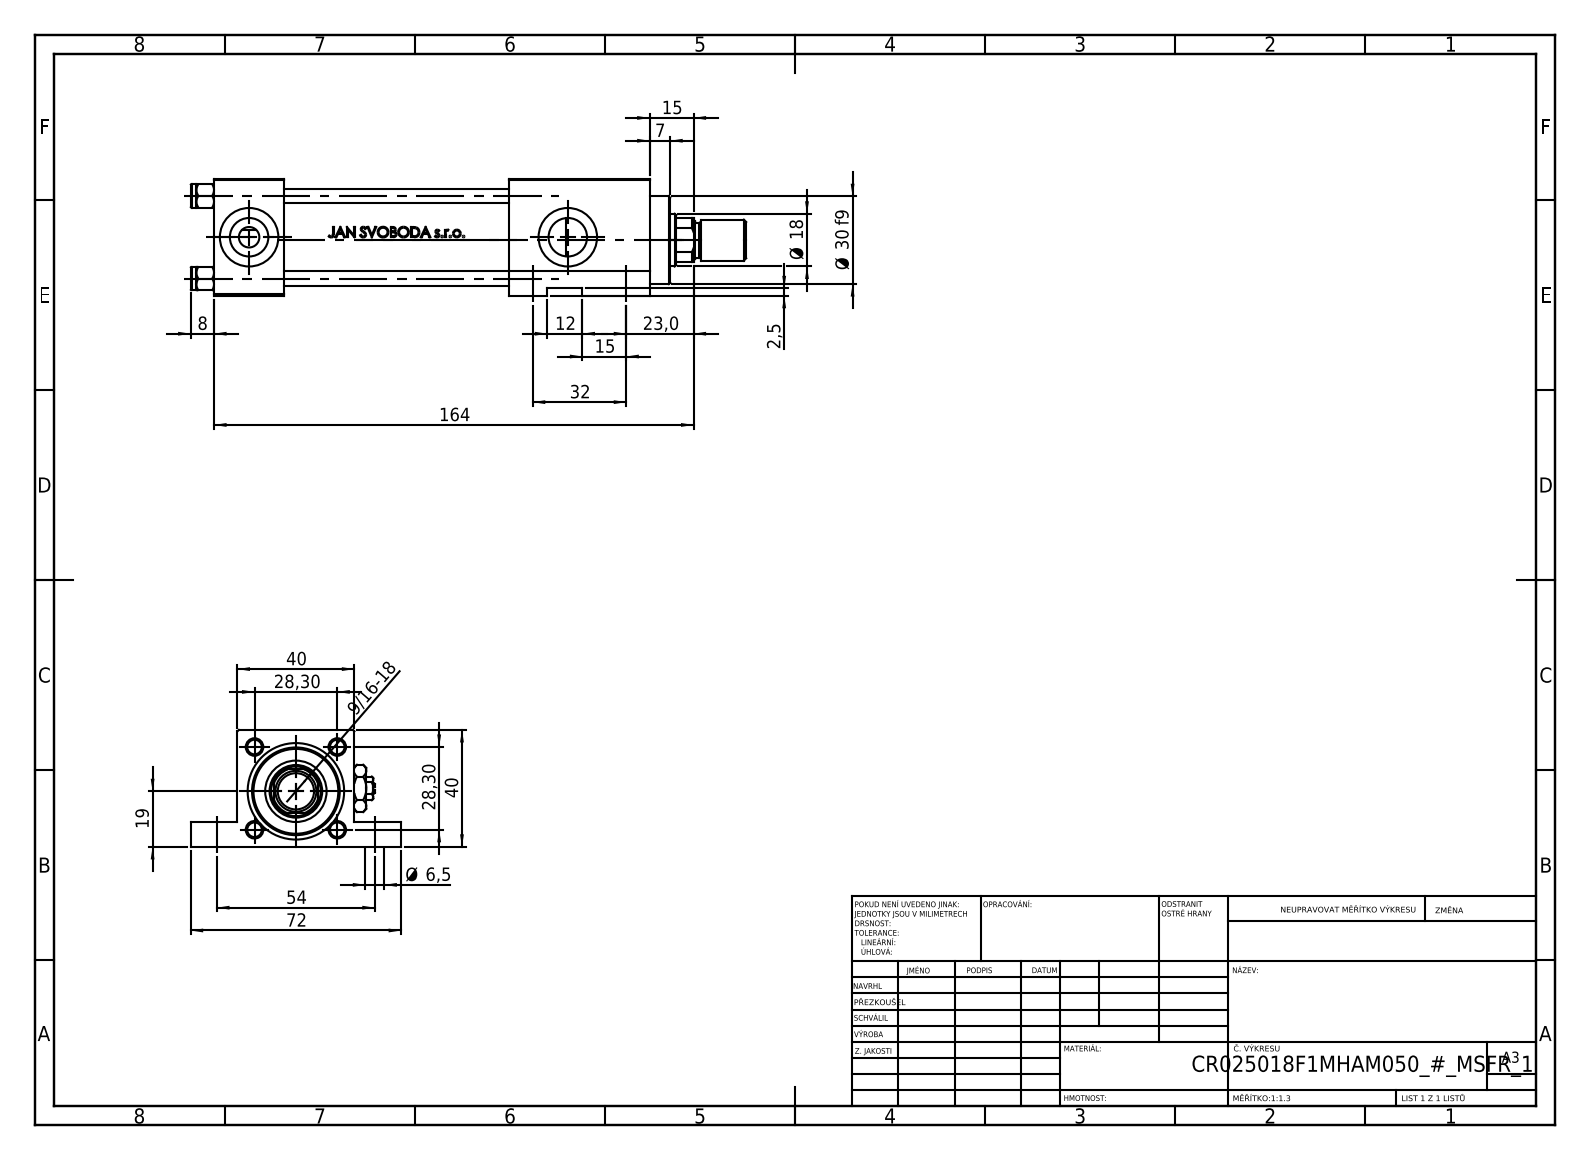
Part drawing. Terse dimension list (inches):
name: V215CR_VCP_F; V215CR_F_TYCINKA; V215CR_F_Body; NUT_M5_F (+3 more)
written by: SolidWorks 2019 (CONFIG_CONTROL_DESIGN)
unit: in
bodies: 13 solids, 1161 faces (463 planar, 132 cylindrical, 566 other)
size: 7.48 × 2.835 × 1.575
volume: 10.99 in³; area: 110.7 in²
holes: 4× ⌀0.197, 4× ⌀0.256, 4× ⌀0.787, 3× ⌀0.518, 2× ⌀0.276, 1× ⌀0.335, 1× ⌀0.709, 1× ⌀0.827, 1× ⌀0.984, 1× ⌀1.181
bosses: 4× ⌀0.315, 1× ⌀1.22, 1× ⌀0.551, 1× ⌀0.472
rounds: 1× R0.335
face distances: 1.575, 0.945, 0.335, 1.24, 3.976, 3.031, 0.236, 1.89, 2.205, 5.866
hole spacings: 1.114, 0.761, 0.816, 1.26, 1.576, 2.126, 2.471, 0.276
